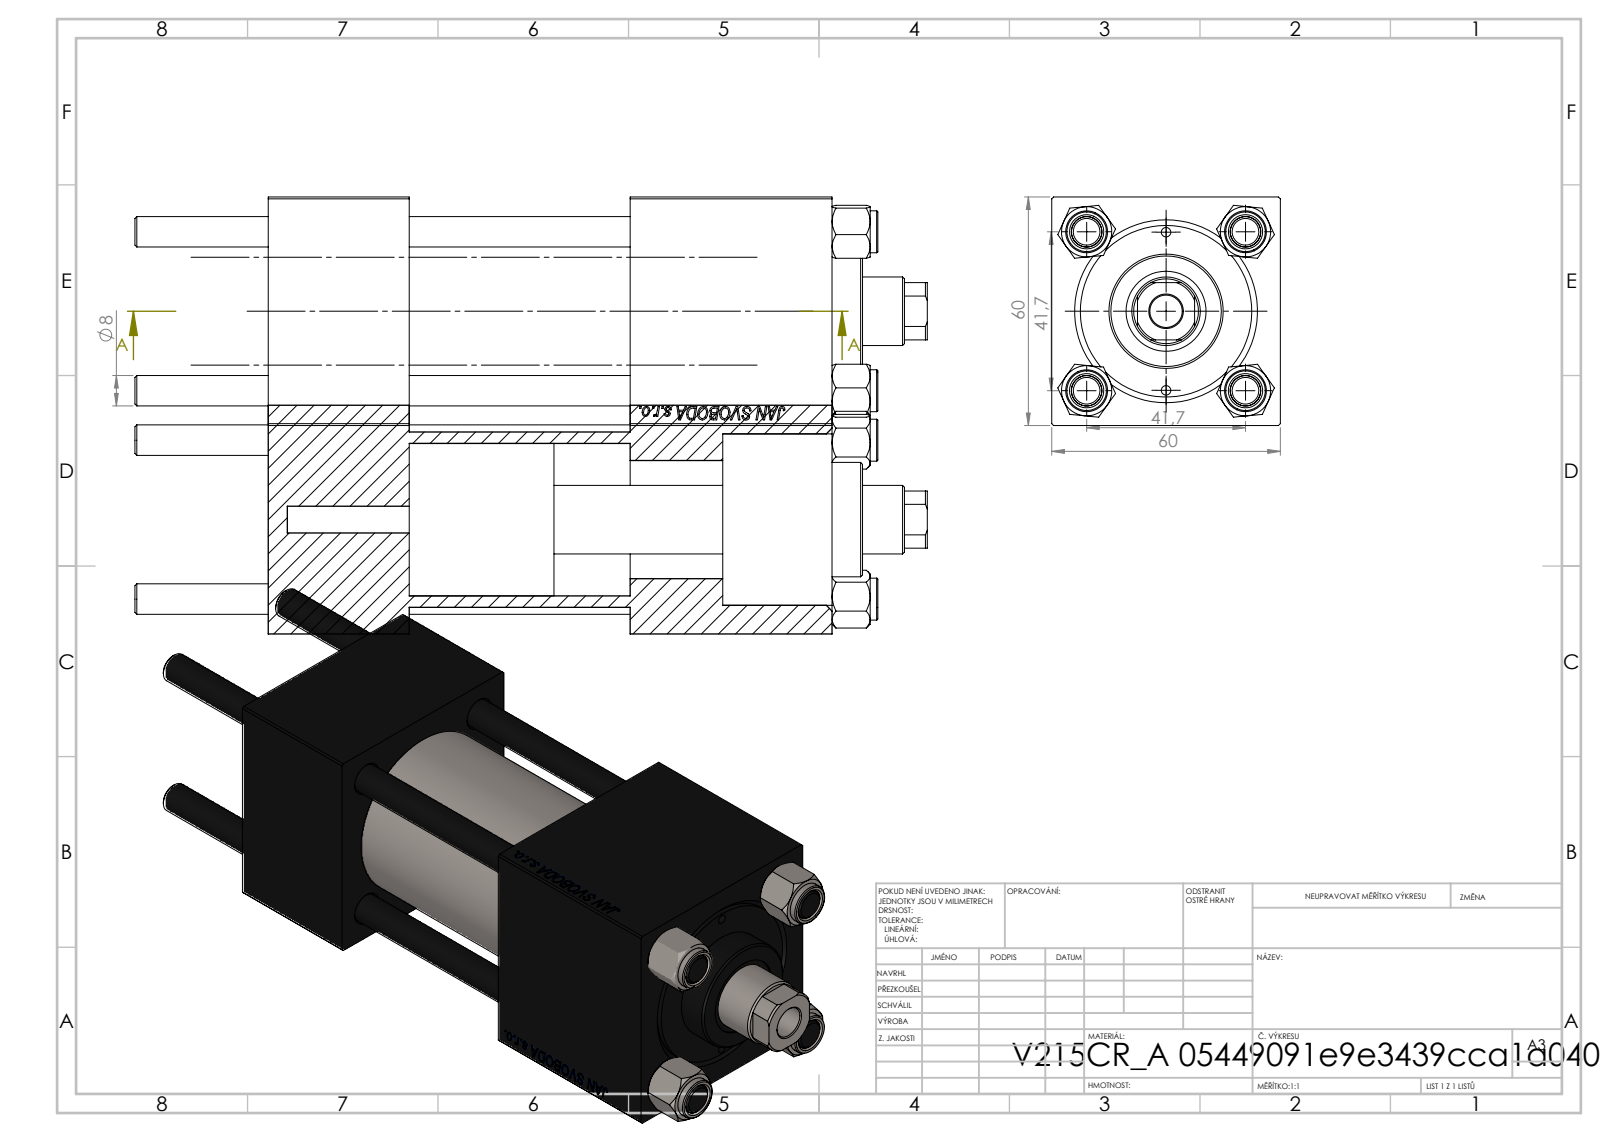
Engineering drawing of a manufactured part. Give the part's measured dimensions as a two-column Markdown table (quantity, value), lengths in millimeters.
| quantity | value |
| --- | --- |
| part name | V215CR_BODY_A; CR025_012_A_0_G_A_G_M_020_+#_##_TYCINKA; NUT_M5; V215CR_VCP (+1 more) |
| STEP written by | SolidWorks 2019 (CONFIG_CONTROL_DESIGN) |
| units | millimeters |
| bodies | 11 solids, 1141 faces (523 planar, 82 cylindrical, 536 other) |
| overall size | 208 × 60 × 60 |
| volume | 413 850 mm³ |
| surface area | 114 085 mm² |
| round holes (diameter × count) | 8 × 4, 2.5 × 2, 7 × 2, 16.66 × 2, 24 × 2, 8.5 × 1, 18 × 1, 21 × 1, 31 × 1, 40 × 1, 45 × 1 |
| round bosses / shafts (diameter × count) | 11 × 4, 46 × 1, 30 × 1 |
| partial cylindrical surfaces (radius × count) | 8.5 × 1 |
| main face-to-face distances | 60, 37, 148, 111, 58, 53, 95, 119.3, 82.3, 24.3 |
| hole center spacings | 20.85, 29.49, 41.7, 46.53, 20.75, 58.97, 41.5, 92.5 |
